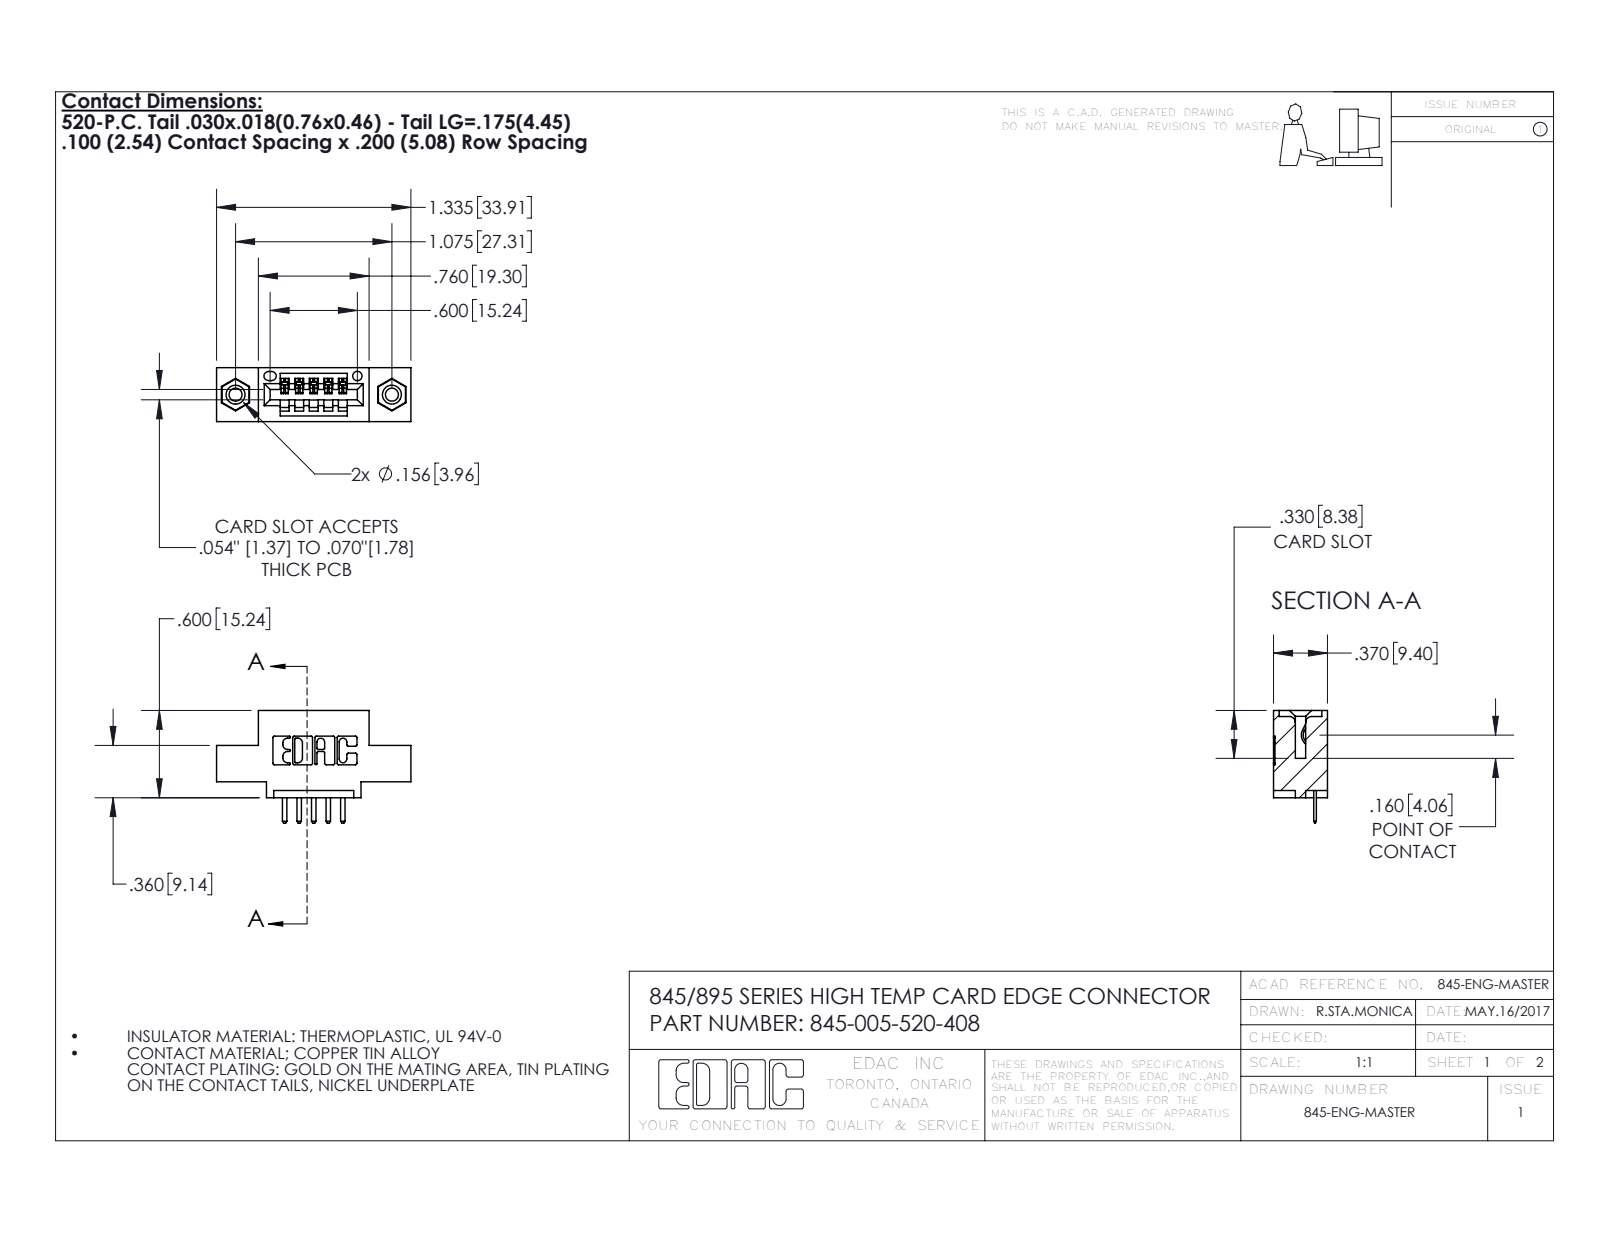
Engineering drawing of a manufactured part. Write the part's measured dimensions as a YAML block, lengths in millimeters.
part_name: "345-250-001_345-250-003-102; 345-292-001_345-293-120; 345 Part_0.110 Offset - 0.156 Dia-TI; 345-005-520-408"
step_written_by: "SolidWorks 2016 (CONFIG_CONTROL_DESIGN)"
units: millimeters
bodies: {solids: 8, faces: 500, planar: 326, cylindrical: 158, other: 16}
overall_size: [33.9, 19.7, 9.4]
volume: 2820
surface_area: 3303
round_holes:
  - {diameter: 2.3, count: 2}
  - {diameter: 3.2, count: 2}
  - {diameter: 4, count: 2}
  - {diameter: 1.6, count: 1}
round_bosses_or_shafts:
  - {diameter: 3.9, count: 2}
partial_cylinders:
  - {radius: 0.3, count: 22}
  - {radius: 0.3, count: 12}
  - {radius: 0.2, count: 10}
  - {radius: 0.2, count: 6}
  - {radius: 0.8, count: 6}
  - {radius: 0.7, count: 3}
  - {radius: 0.8, count: 2}
  - {radius: 1, count: 2}
face_to_face_distances: [5.1, 9.4, 2.5, 1.8, 7.6, 0.6, 6.4, 1.5, 4.1, 1]
hole_center_spacings: [6.9, 21.5, 27.3]
